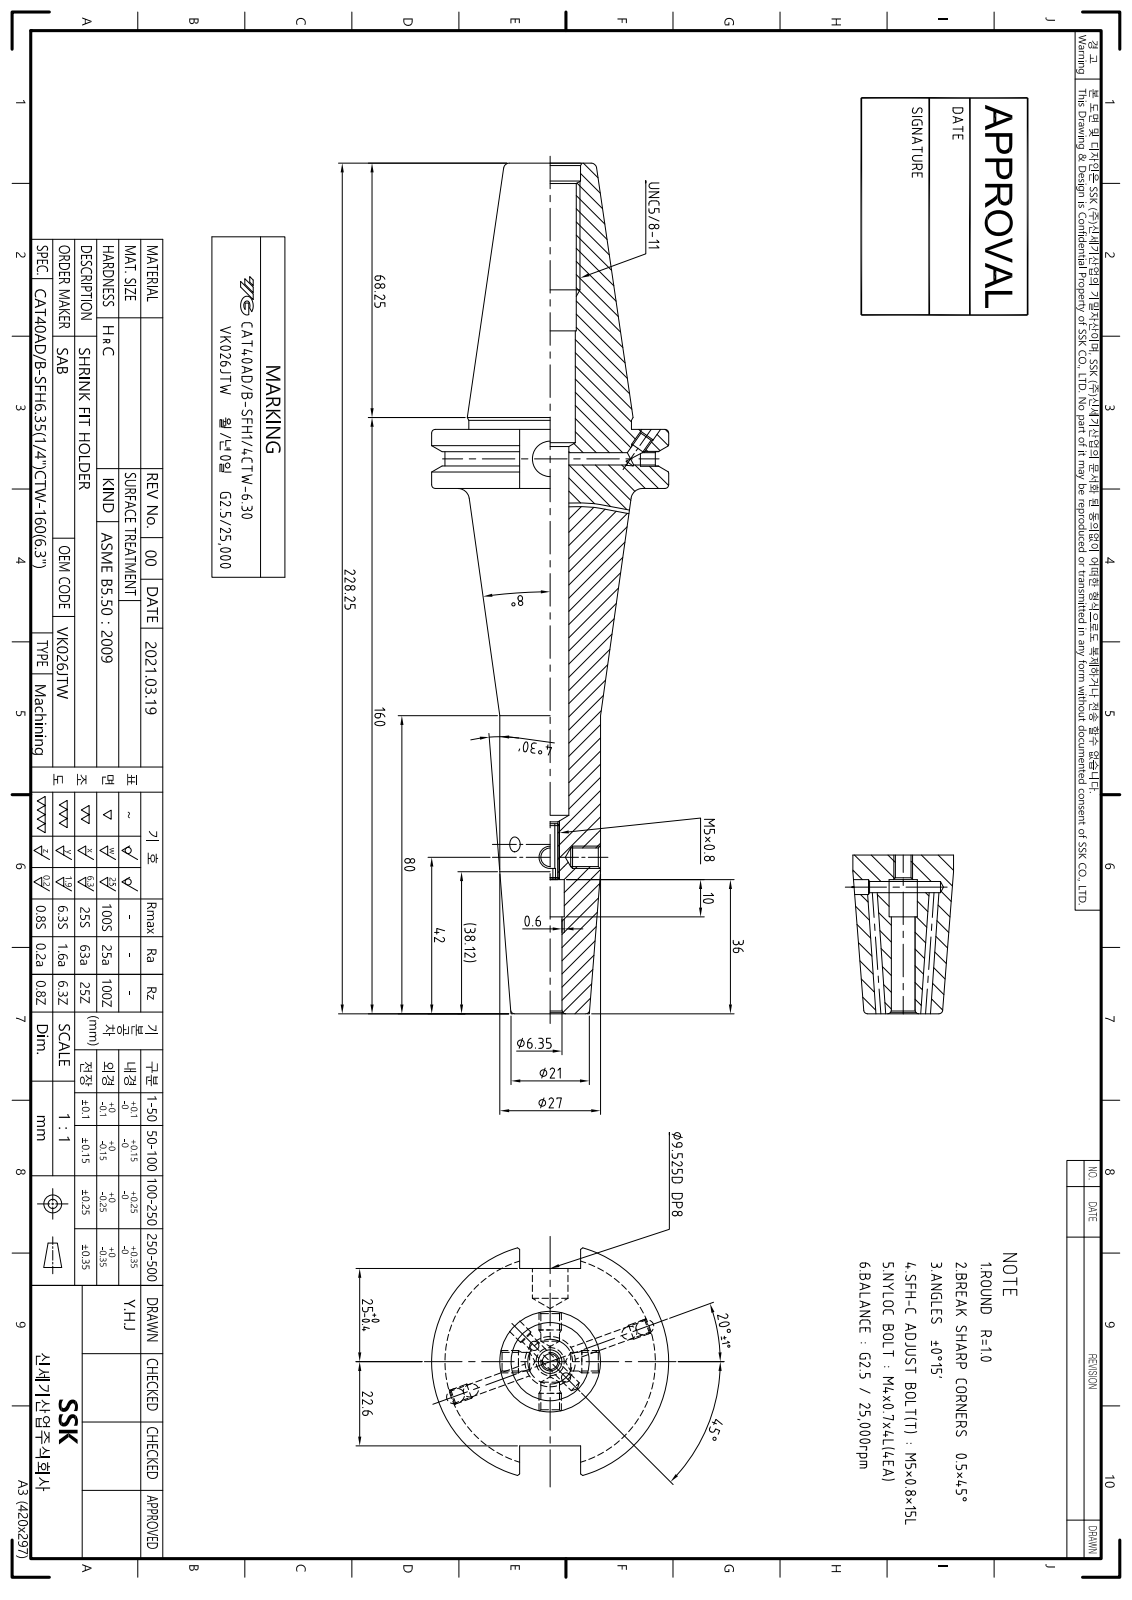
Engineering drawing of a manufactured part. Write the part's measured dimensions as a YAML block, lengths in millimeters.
part_name: "LO-CAT40ADB-SFH6.35CTW-160"
step_written_by: "Autodesk Inventor 2022 (AUTOMOTIVE_DESIGN)"
units: millimeters
bodies: {solids: 1, faces: 94, planar: 39, cylindrical: 32, other: 23}
overall_size: [228.25, 63.5, 61.09]
volume: 195663
surface_area: 37156
round_holes:
  - {diameter: 3.24, count: 4}
  - {diameter: 2.5, count: 2}
  - {diameter: 4, count: 2}
  - {diameter: 4.2, count: 2}
  - {diameter: 4.3, count: 1}
  - {diameter: 6.35, count: 1}
  - {diameter: 7.55, count: 1}
  - {diameter: 9.53, count: 1}
  - {diameter: 10, count: 1}
  - {diameter: 13, count: 1}
  - {diameter: 13.39, count: 1}
  - {diameter: 16.3, count: 1}
round_bosses_or_shafts:
  - {diameter: 63.5, count: 1}
  - {diameter: 43.6, count: 1}
  - {diameter: 27, count: 1}
partial_cylinders:
  - {radius: 28.15, count: 1}
face_to_face_distances: [15.88, 156.83, 140.95, 47.6, 16.38, 71.42, 87.3, 228.25, 77.47, 6.05]
